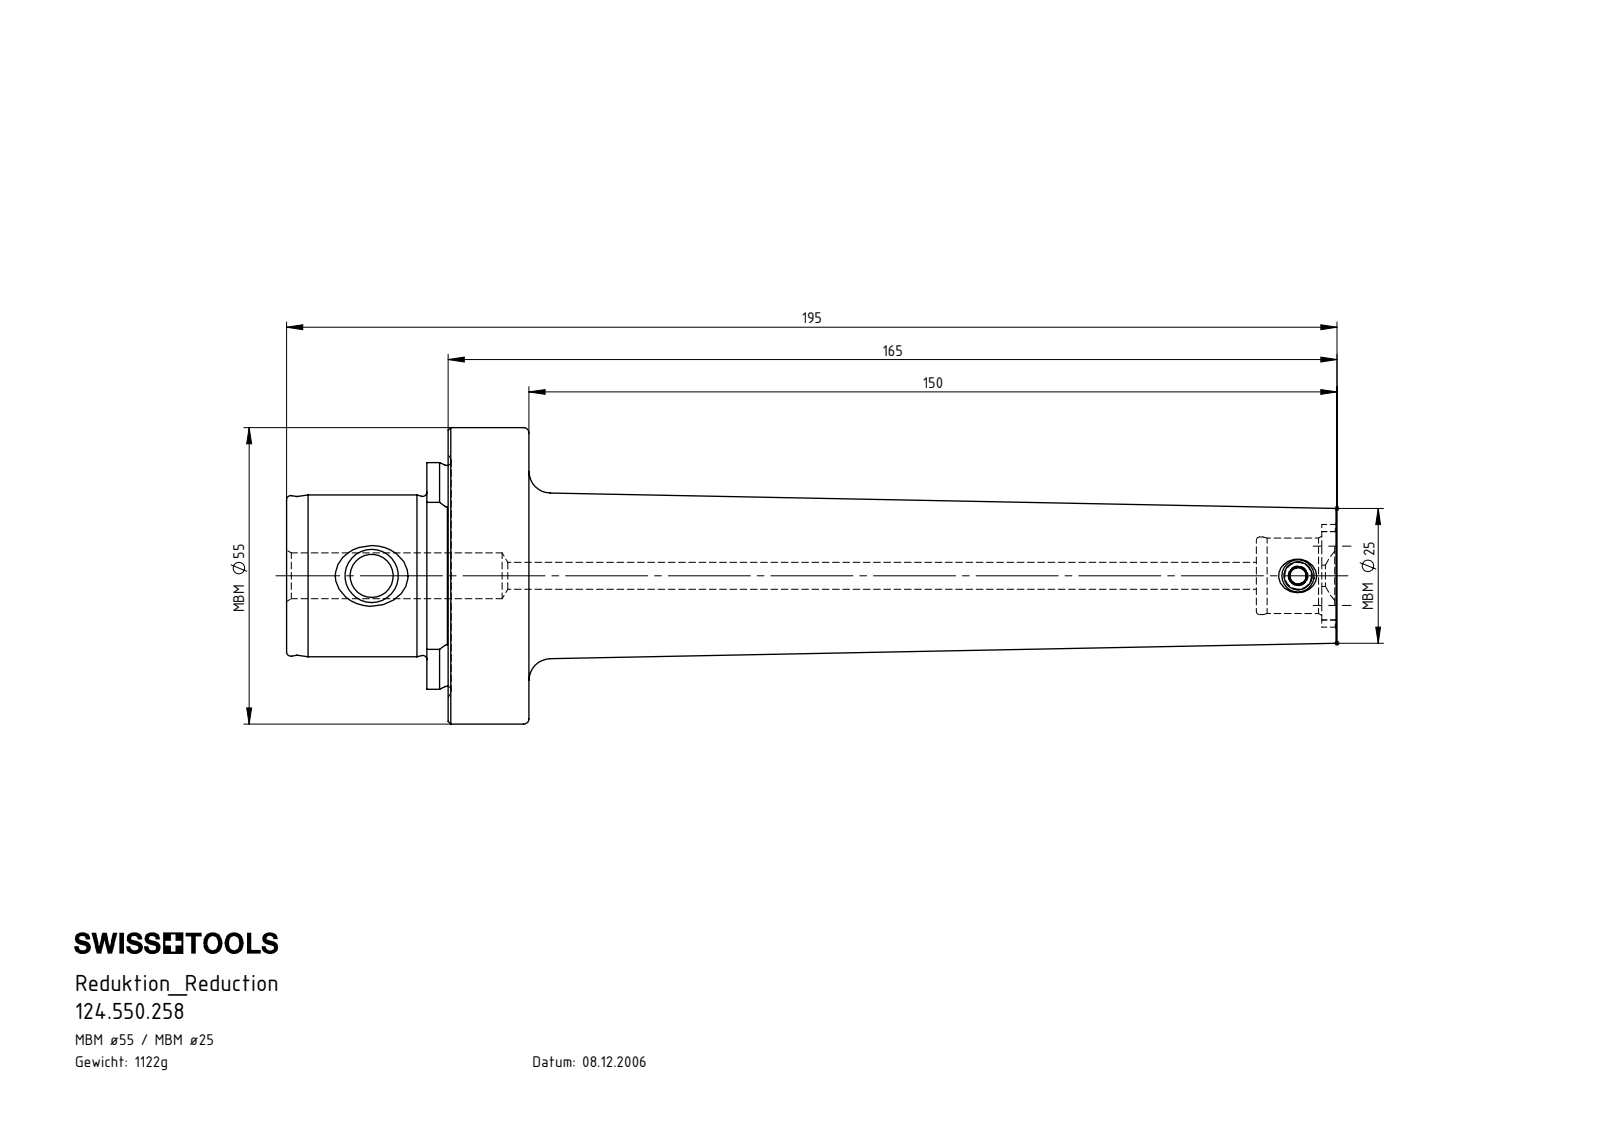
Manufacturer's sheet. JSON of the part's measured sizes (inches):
{"part_name": "124.550.258; MB2-ER1.001.008_A; MB5-MB2.K01.165_C", "step_written_by": "SolidWorks 2017 (CONFIG_CONTROL_DESIGN)", "units": "inches", "bodies": {"solids": 2, "faces": 136, "planar": 31, "cylindrical": 34, "other": 71}, "overall_size": [7.677, 2.165, 2.165], "volume_in3": 8.719, "surface_area_in2": 42.24, "round_holes": [[0.118, 1], [0.197, 1], [0.207, 1], [0.315, 1], [0.335, 1], [0.551, 1], [0.567, 1]], "round_bosses_or_shafts": [[2.165, 1], [1.181, 1], [0.236, 1]], "partial_cylinders_radius": [[0.106, 4], [0.315, 1], [0.375, 1], [0.828, 1]], "face_to_face_distances": [0.591, 1.181, 1.772, 1.026, 0.156, 0.746, 5.906, 1.175, 0.15, 0.596], "hole_center_spacings": [6.77]}
